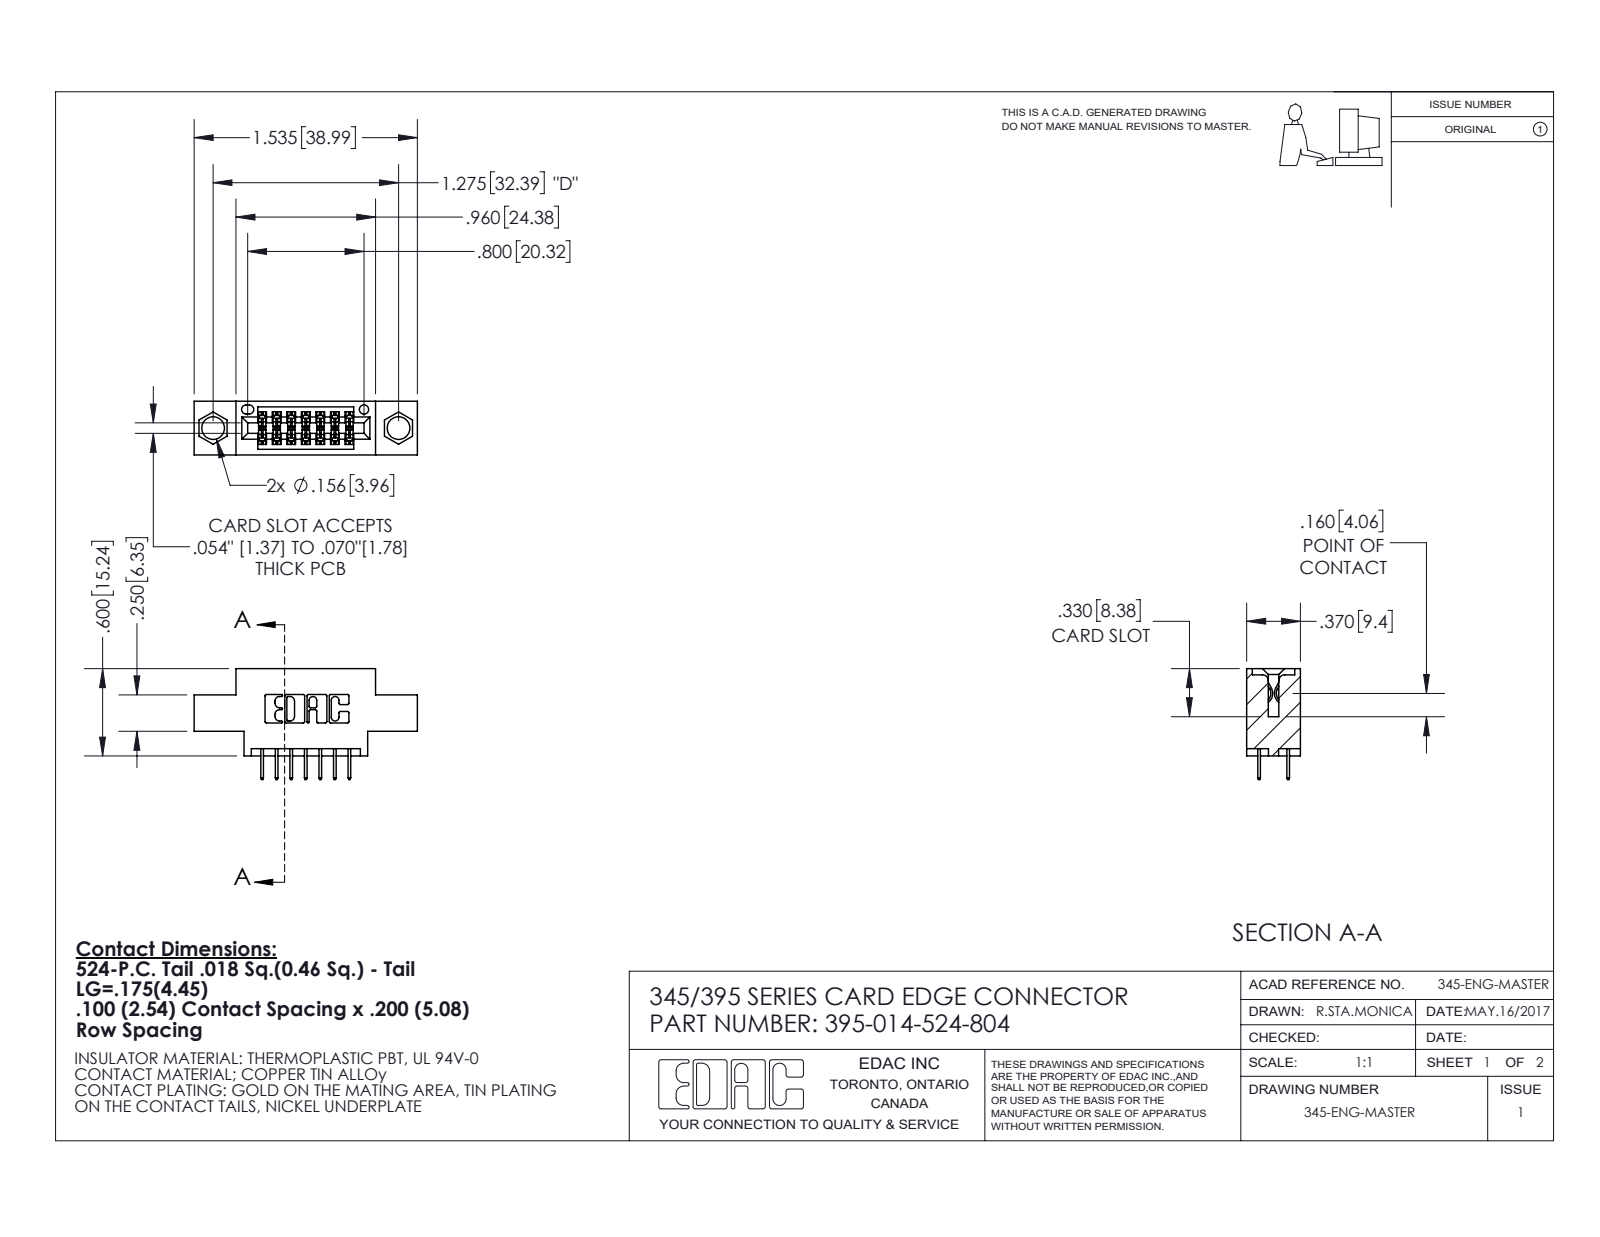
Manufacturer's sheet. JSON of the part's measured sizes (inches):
{"part_name": "345-292-001_345-293-124; 395-014-524-804; 345 Part_0.170 Offset - 0.156 Dia-TI", "step_written_by": "SolidWorks 2020 (CONFIG_CONTROL_DESIGN)", "units": "inches", "bodies": {"solids": 15, "faces": 900, "planar": 644, "cylindrical": 256, "other": 0}, "overall_size": [1.535, 0.762, 0.37], "volume_in3": 0.197, "surface_area_in2": 6.237, "round_holes": [[0.156, 2], [0.064, 1]], "partial_cylinders_radius": [[0.006, 28], [0.01, 22], [0.007, 6], [0.031, 6], [0.026, 3], [0.014, 2], [0.019, 2], [0.022, 2]], "face_to_face_distances": [0.2, 0.37, 0.1, 0.072, 0.298, 0.3, 0.098, 0.272, 0.025, 0.06], "hole_center_spacings": [0.27, 1.045, 1.275]}
